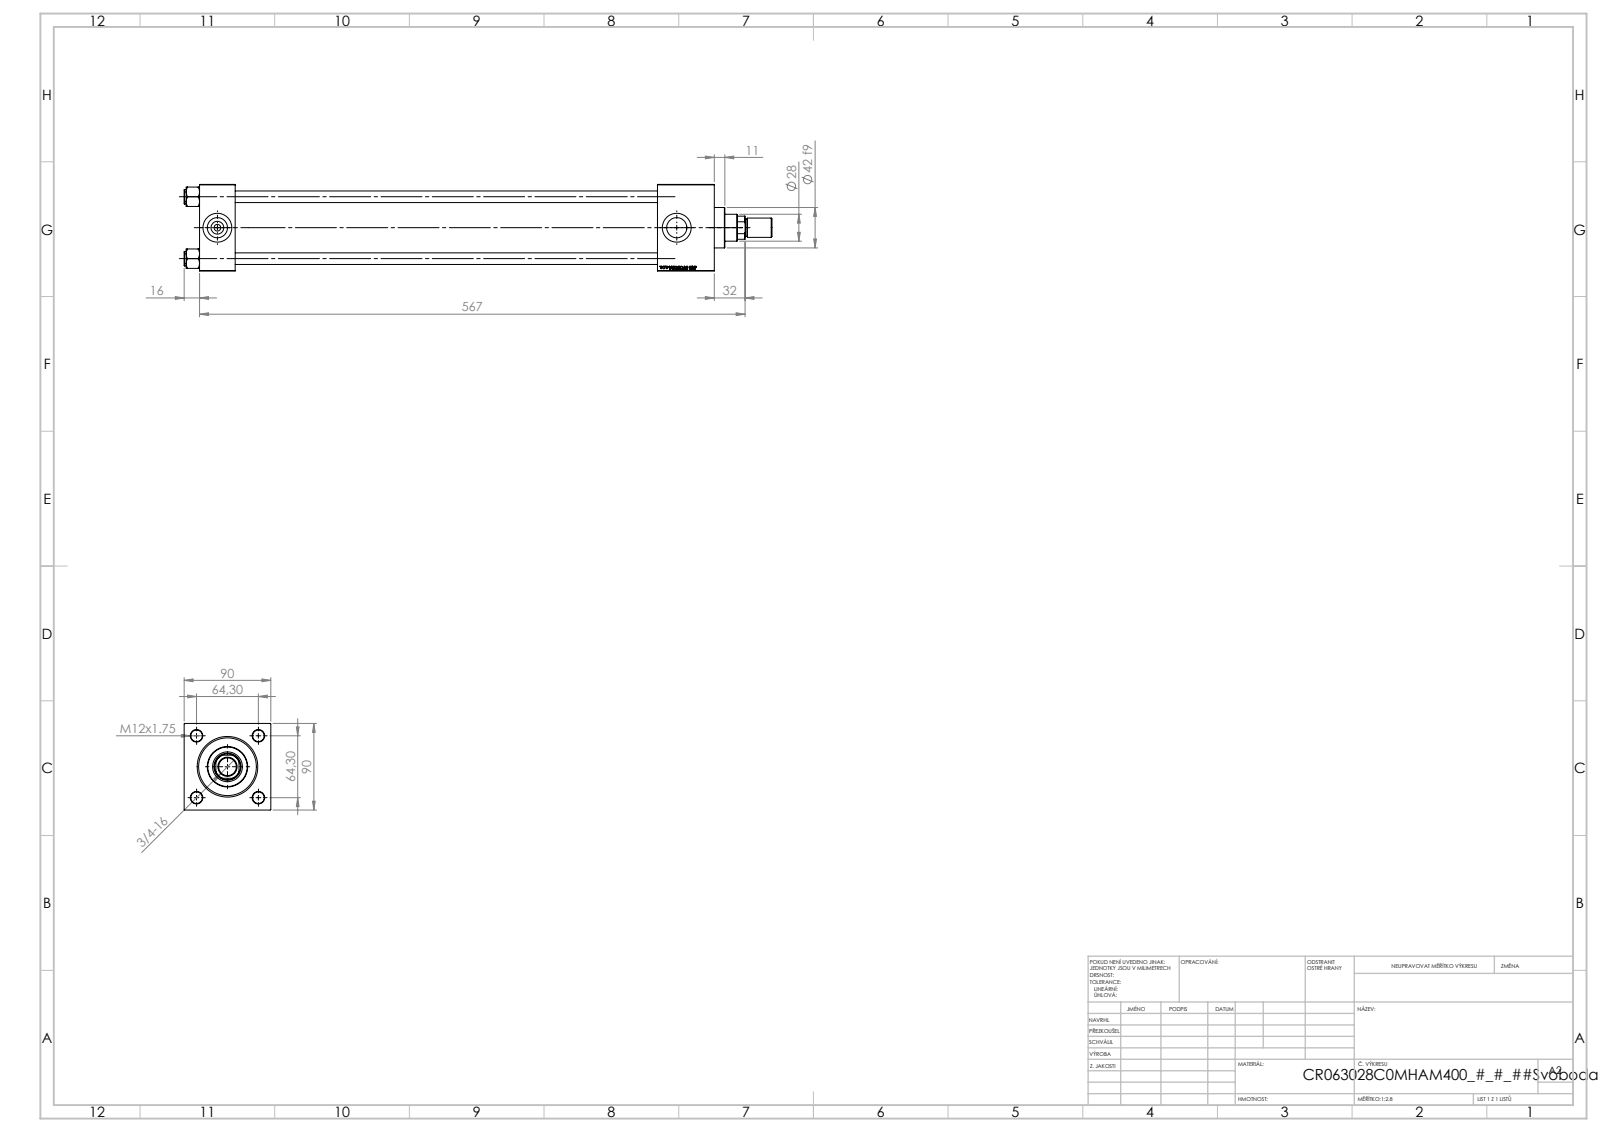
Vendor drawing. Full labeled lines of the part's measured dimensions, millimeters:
Part name (STEP PRODUCT): V215_VC_A; V215CR_VCP_C; NUT_M5_C; V215CR_C_Body (+2 more)
STEP written by: SolidWorks 2019 (CONFIG_CONTROL_DESIGN)
Units: millimetres
Bodies: 12 solids, 1162 faces (530 planar, 90 cylindrical, 542 other)
Overall size (bounding box): 611 × 90 × 90
Volume: 1 598 000 mm³ · Surface area: 429 873 mm²
Round holes (diameter × count): ⌀12 ×4, ⌀7 ×2, ⌀20.96 ×2, ⌀30 ×2, ⌀18.5 ×1, ⌀28 ×1, ⌀31 ×1, ⌀50 ×1, ⌀60 ×1, ⌀63 ×1
Round bosses / shafts (diameter × count): ⌀15 ×4, ⌀69 ×1, ⌀42 ×1, ⌀20 ×1, ⌀18 ×1
Partial cylindrical surfaces — rounded edges, fillets, slot ends (radius × count): R13.5 ×1
Main face-to-face distances: 90, 37, 535, 498, 476, 439, 59, 506.3, 469.3, 30.3
Hole centre spacings: 45.47, 64.3, 90.93, 477.5
